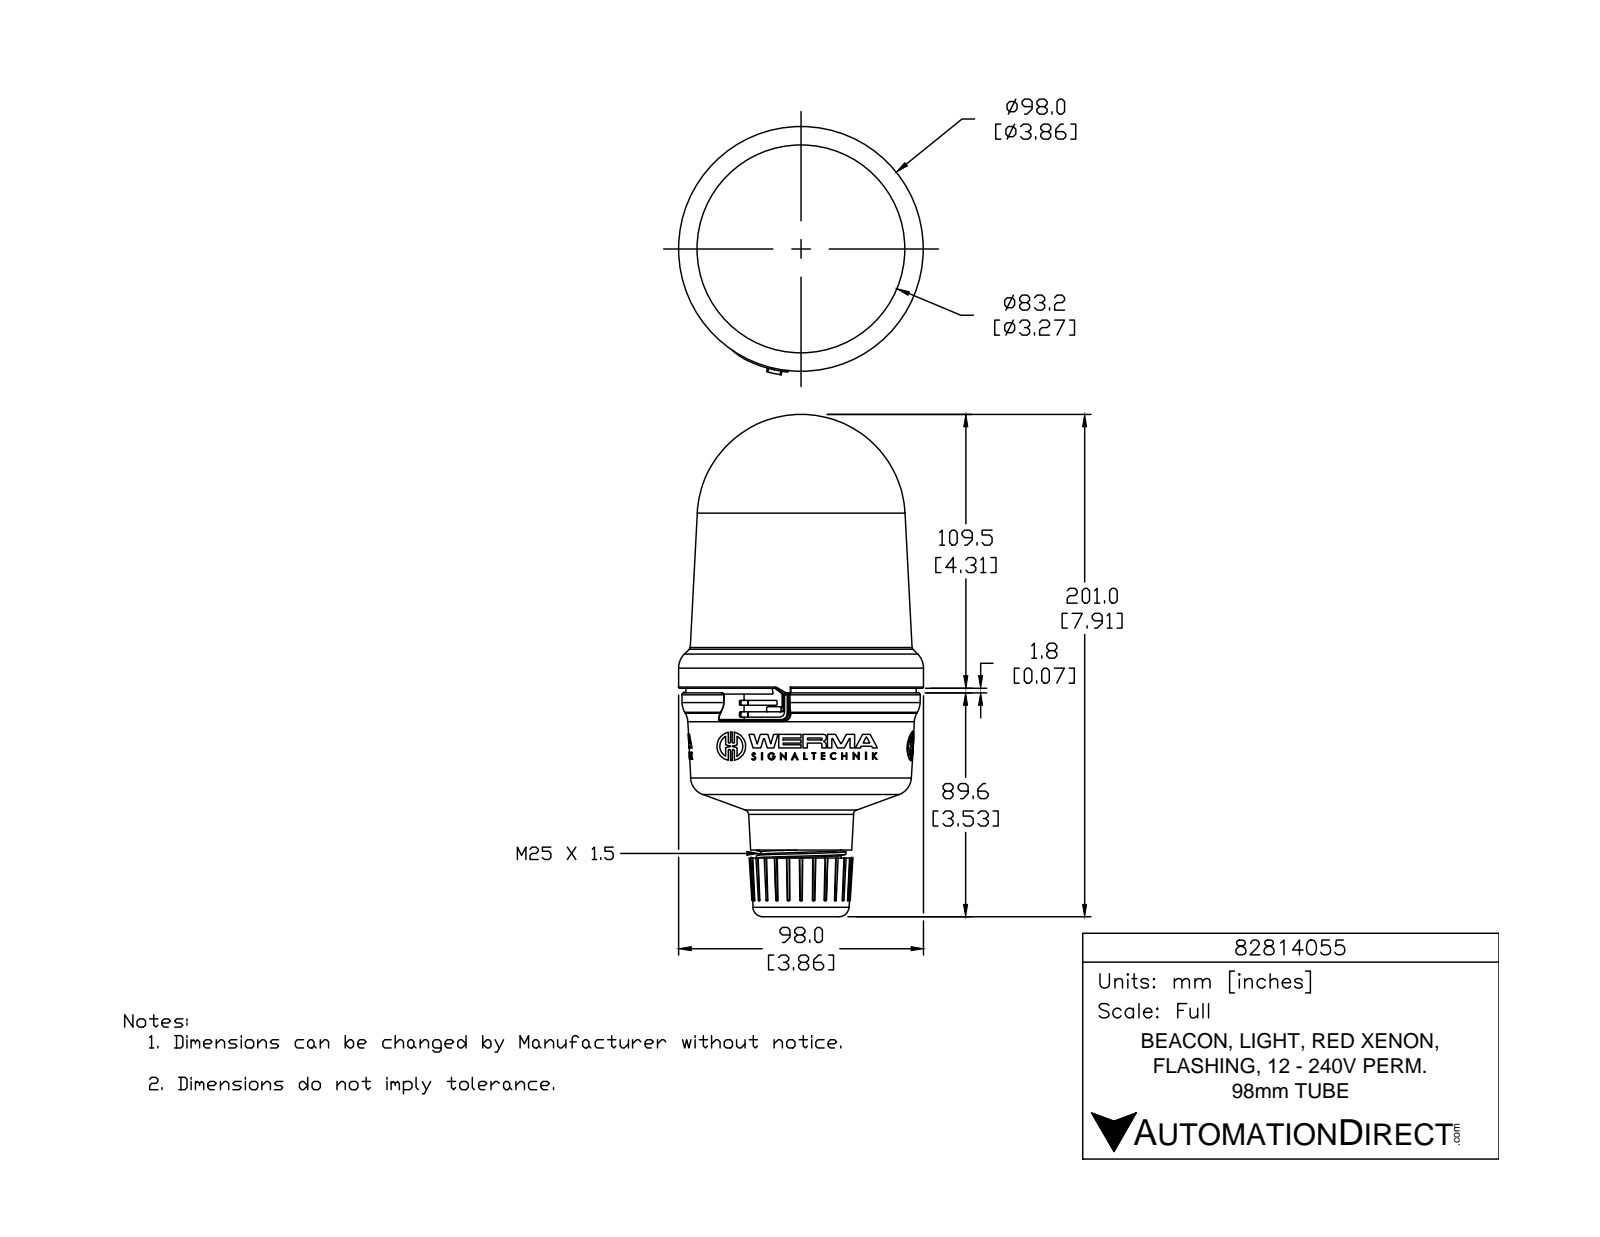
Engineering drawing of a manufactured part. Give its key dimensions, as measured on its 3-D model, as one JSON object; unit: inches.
{"part_name": "82814055", "step_written_by": "SolidWorks 2015 (AUTOMOTIVE_DESIGN)", "units": "inches", "bodies": {"solids": 1, "faces": 1006, "planar": 554, "cylindrical": 189, "other": 263}, "overall_size": [7.914, 3.912, 3.858], "volume_in3": 54.7, "surface_area_in2": 91.39, "round_holes": [[0.078, 3], [1.013, 1], [1.024, 1]], "round_bosses_or_shafts": [[0.452, 3], [0.113, 3], [3.858, 1], [1.409, 1], [1.261, 1]], "partial_cylinders_radius": [[0.02, 12], [0.007, 9], [0.007, 6], [0.016, 6], [0.016, 6], [0.016, 6], [0.262, 6], [0.006, 3]], "face_to_face_distances": [2.214, 0.462, 2.676, 0.335, 0.127, 2.548, 2.603, 2.476, 2.141, 0.073]}
